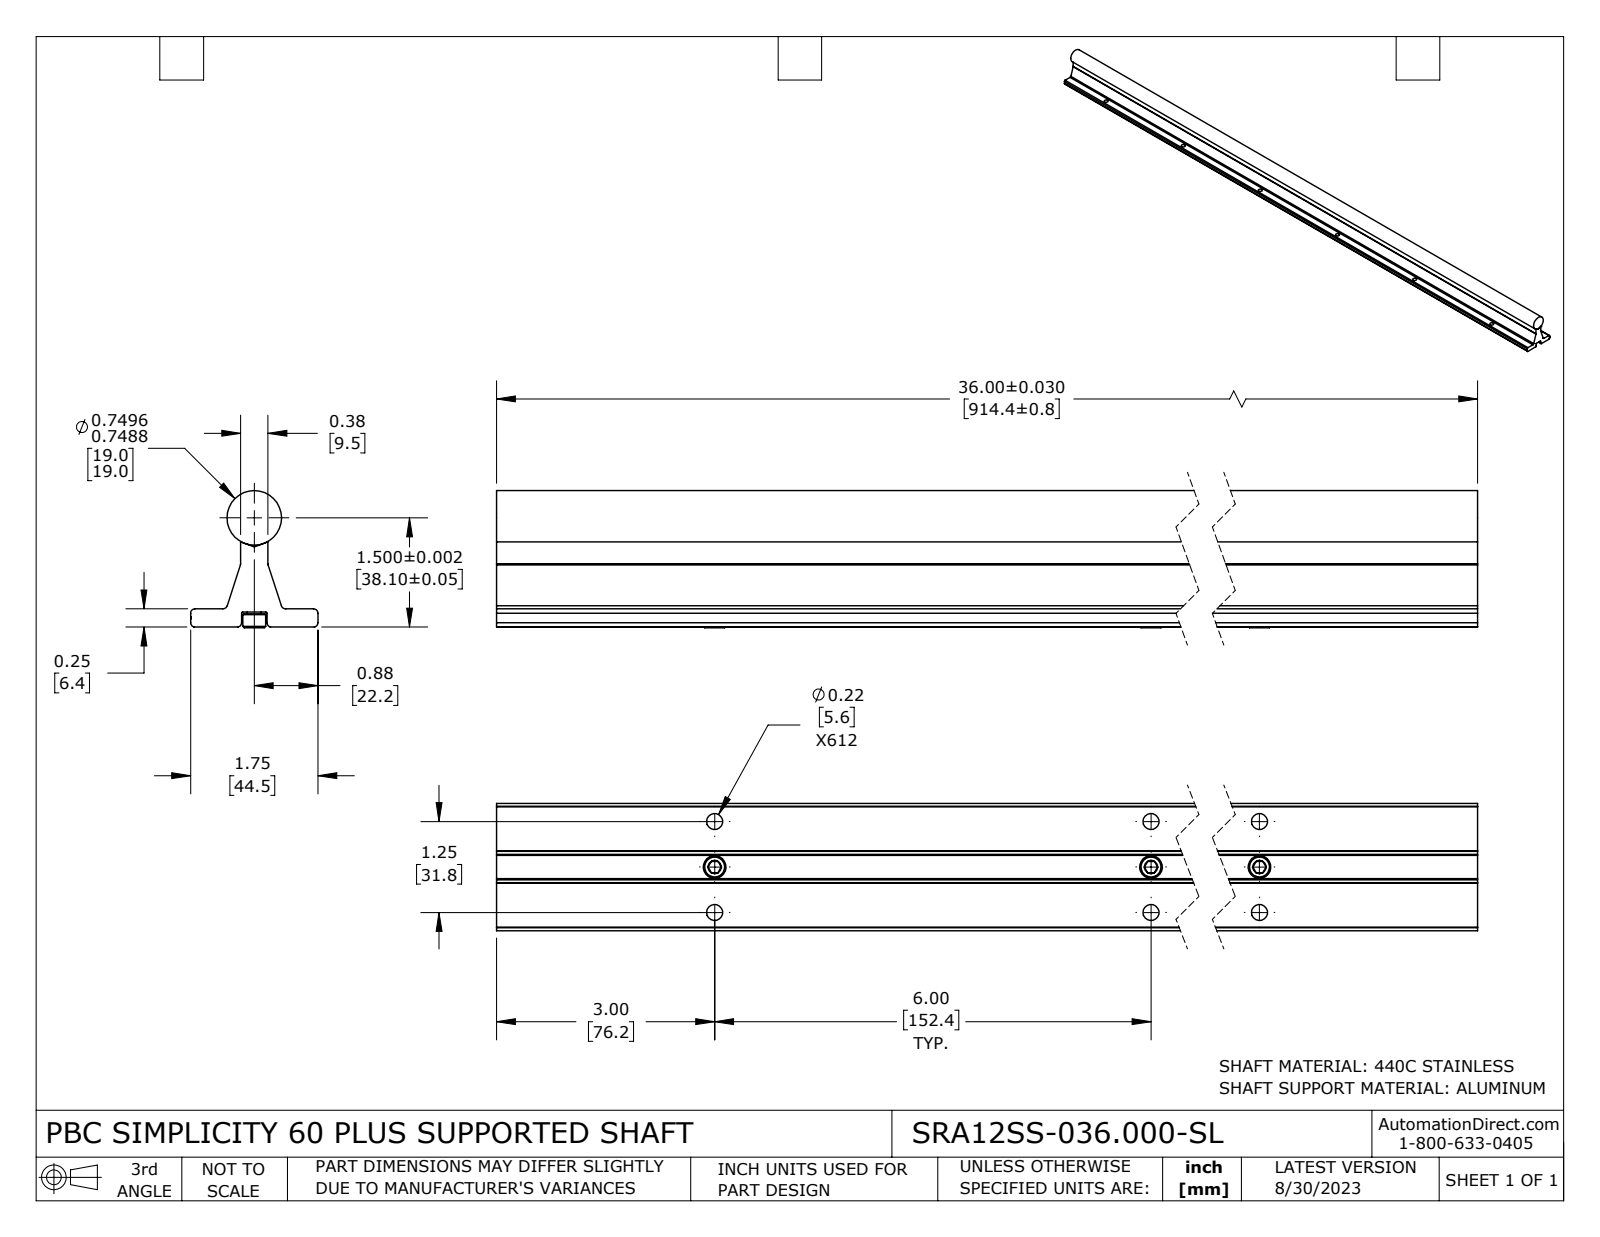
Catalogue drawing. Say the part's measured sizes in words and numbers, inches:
The part is named "SRA12SS-036.000-SL". Its 3-D file was written by "SolidWorks 2021 (CONFIG_CONTROL_DESIGN)". It is 8 solids with 281 faces: 93 planar, 98 cylindrical and 90 other. Overall it measures 36 by 1.885 by 1.75 inches. Its volume is 45.12 cubic inches and its surface area 307.8 square inches. Round holes: 18 of diameter 0.221, 6 of diameter 0.169, 6 of diameter 0.25. Round bosses or shafts: 6 of diameter 0.312, 6 of diameter 0.19, 1 of diameter 0.75. Partial cylindrical surfaces (rounded edges, fillets, slot ends): 6 of radius 0.06, 2 of radius 0.015, 2 of radius 0.062, 2 of radius 0.063. The main face-to-face distances are 0.25, 0.205, 0.045, 0.375, 0.012, 0.363, 0.688, 0.7, 1.05, 1.063. The hole center spacings are 6.033, 12.016, 6, 0.625, 12, 18.011, 6.129, 18.
